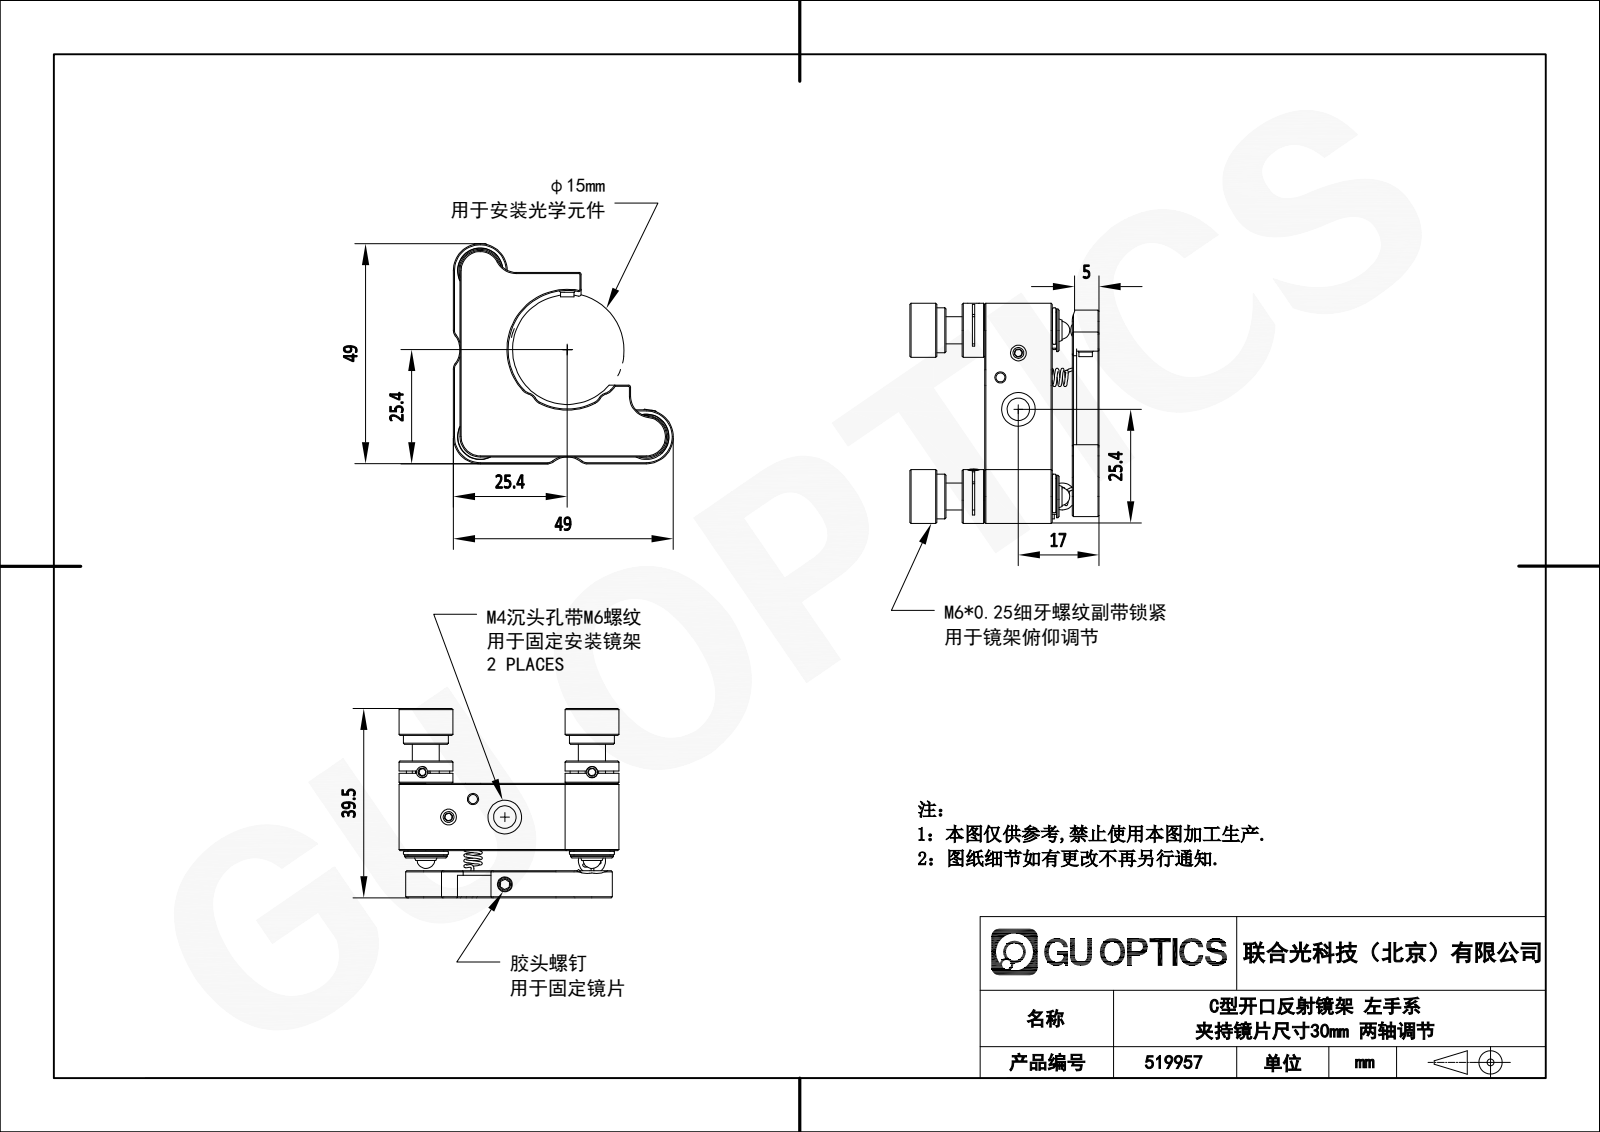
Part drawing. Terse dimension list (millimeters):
written by: SolidWorks 2021 (CONFIG_CONTROL_DESIGN)
unit: mm
bodies: 0 solids, 465 faces (151 planar, 126 cylindrical, 188 other)
size: 49 × 49 × 40.6
holes: 4× ⌀2.5, 2× ⌀4, 2× ⌀6, 2× ⌀7.5, 1× ⌀3.3, 1× ⌀5, 1× ⌀5.5
bosses: 7× ⌀3, 3× ⌀10, 3× ⌀9.5, 2× ⌀12, 2× ⌀6, 2× ⌀4, 1× ⌀8.9
rounds: 7× R4.5, 4× R0.5, 4× R2, 4× R2.5, 4× R5, 2× R0.2, 2× R1.25, 2× R10
face distances: 6, 24.08, 18.08, 3.08, 9.08, 15, 1.5, 2.25, 2.75, 12
hole spacings: 8.15, 10.5, 14.88, 17.08, 45.51, 7.12, 13.58, 18.96
